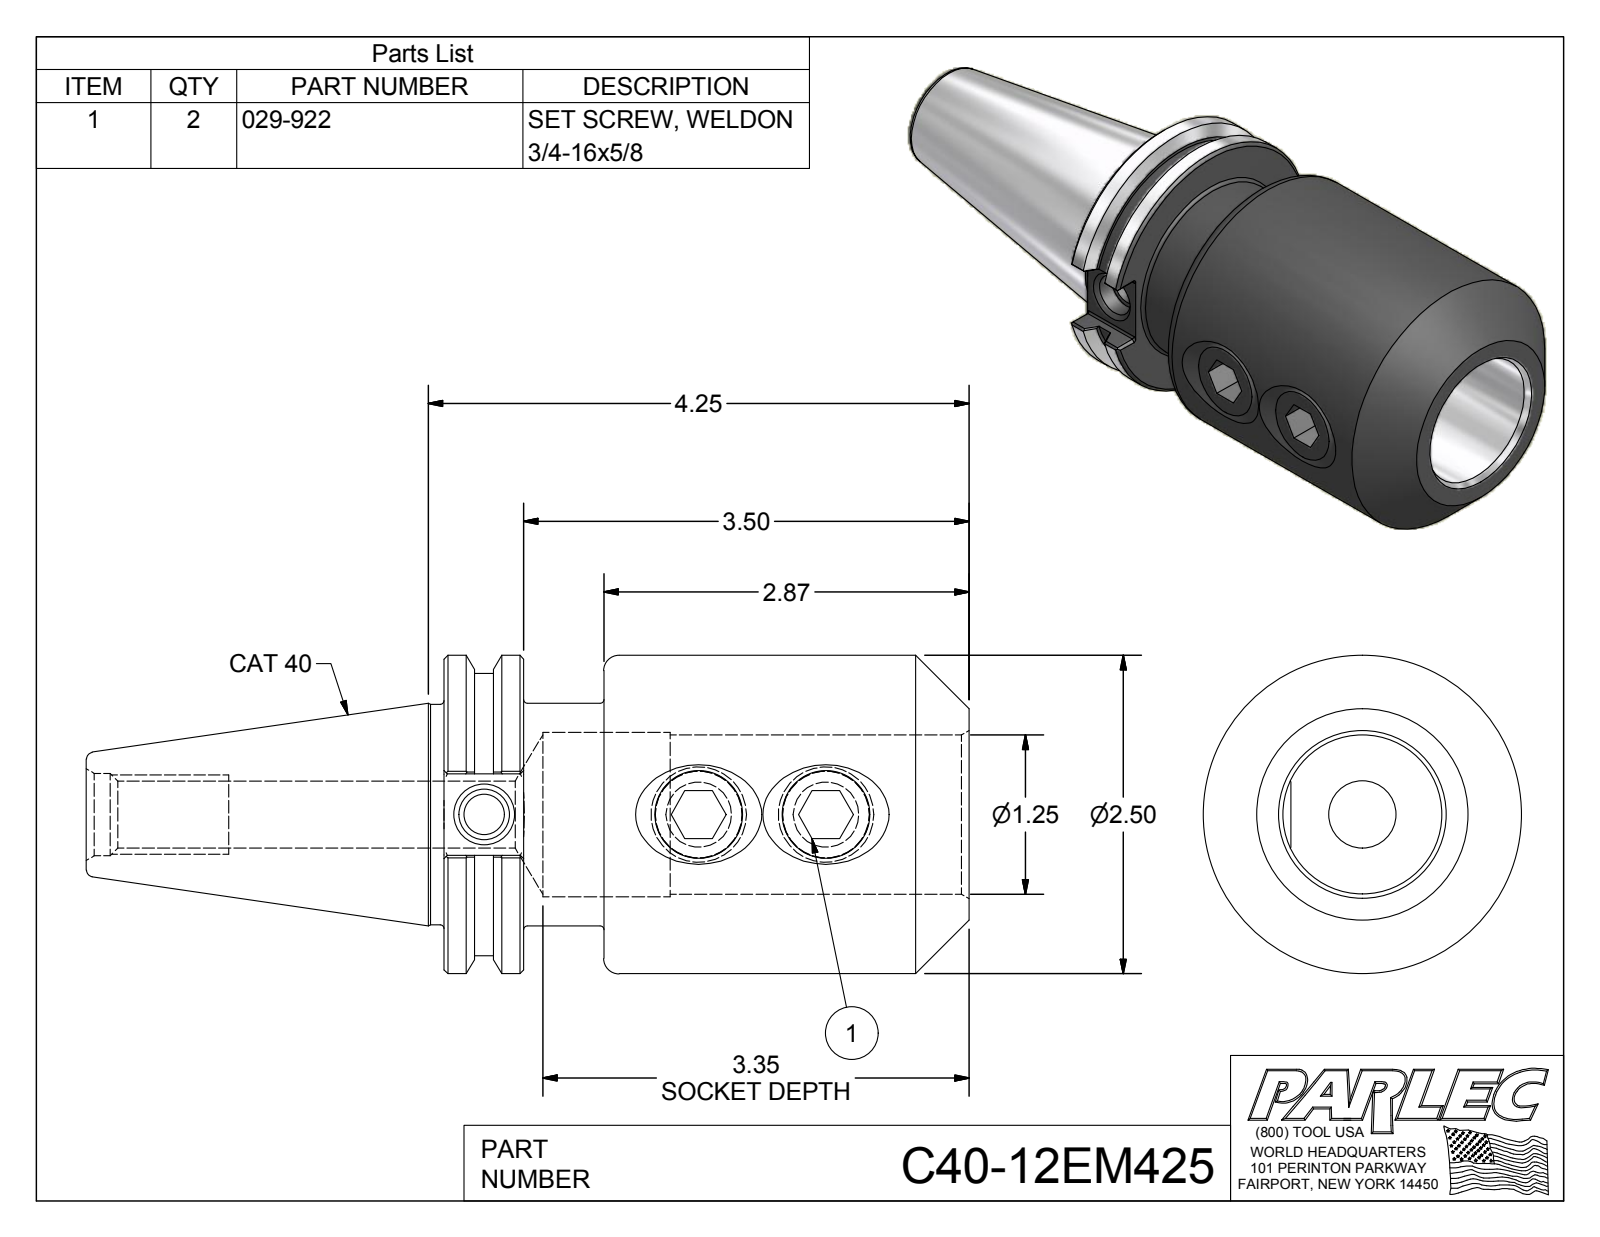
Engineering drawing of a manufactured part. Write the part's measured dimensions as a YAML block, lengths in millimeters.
part_name: "C40-12EM425; c40-12em425-1; 029-922"
step_written_by: "Autodesk Inventor 2012 (AUTOMOTIVE_DESIGN)"
units: millimeters
bodies: {solids: 3, faces: 119, planar: 52, cylindrical: 31, other: 36}
overall_size: [176.2, 63.5, 63.5]
volume: 273800
surface_area: 51140
round_holes:
  - {diameter: 17.3, count: 2}
  - {diameter: 8, count: 1}
  - {diameter: 10.1, count: 1}
  - {diameter: 13.4, count: 1}
  - {diameter: 16.5, count: 1}
  - {diameter: 31.8, count: 1}
  - {diameter: 32.8, count: 1}
round_bosses_or_shafts:
  - {diameter: 19.1, count: 2}
  - {diameter: 63.5, count: 1}
  - {diameter: 56.4, count: 1}
  - {diameter: 44.5, count: 1}
  - {diameter: 43.9, count: 1}
partial_cylinders:
  - {radius: 0.5, count: 12}
face_to_face_distances: [15.9, 31.9, 16, 104.8, 88.9, 72.9, 22, 9.5, 15.9, 36.8]
hole_center_spacings: [25.4, 42.8, 68.2]
